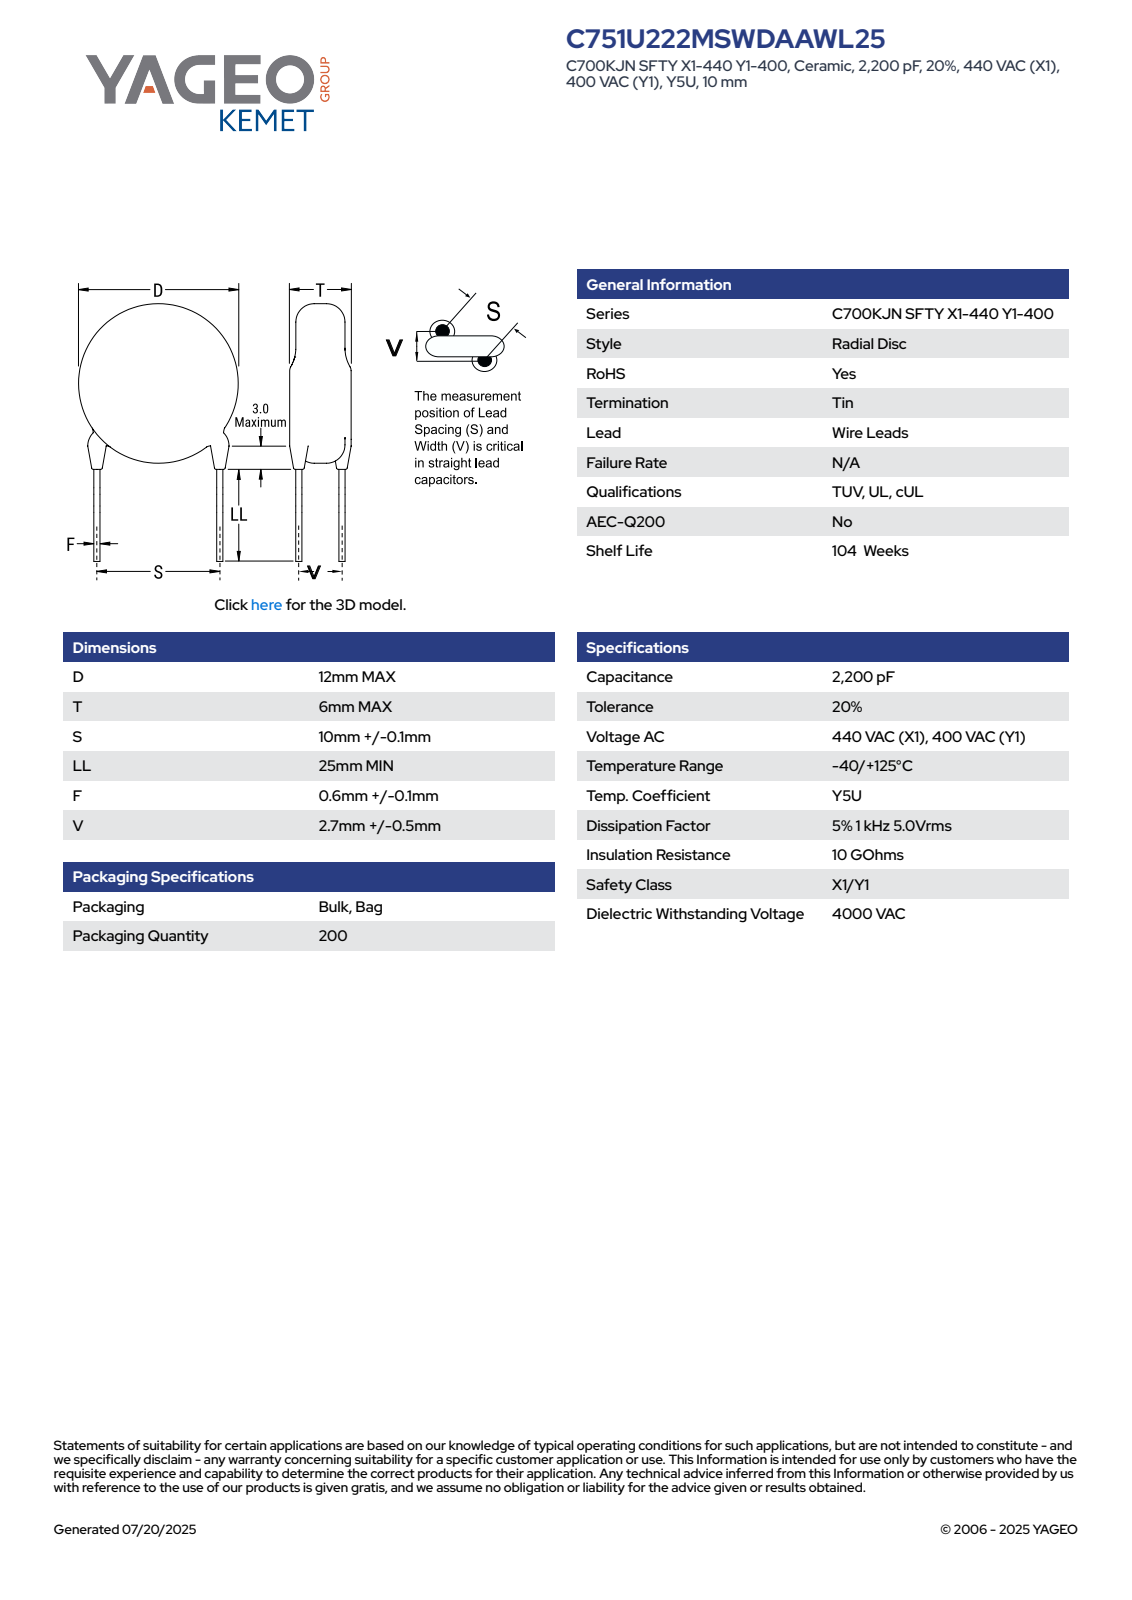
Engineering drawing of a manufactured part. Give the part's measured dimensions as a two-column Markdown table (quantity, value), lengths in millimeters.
| quantity | value |
| --- | --- |
| part name | CCD_KST_12X6_D12T6S10.1LL25F0.7V2.7 |
| STEP written by | SolidWorks 2021 (AUTOMOTIVE_DESIGN) |
| units | millimeters |
| bodies | 4 solids, 80 faces (63 planar, 13 cylindrical, 4 other) |
| overall size | 37.75 × 12 × 6 |
| volume | 690 mm³ |
| surface area | 565 mm² |
| round bosses / shafts (diameter × count) | 1.2 × 4, 0.7 × 2, 12 × 1 |
| main face-to-face distances | 6, 25, 32.66, 7.66, 31.3, 6.3, 1.36, 0.37, 1.1, 5.55 |
